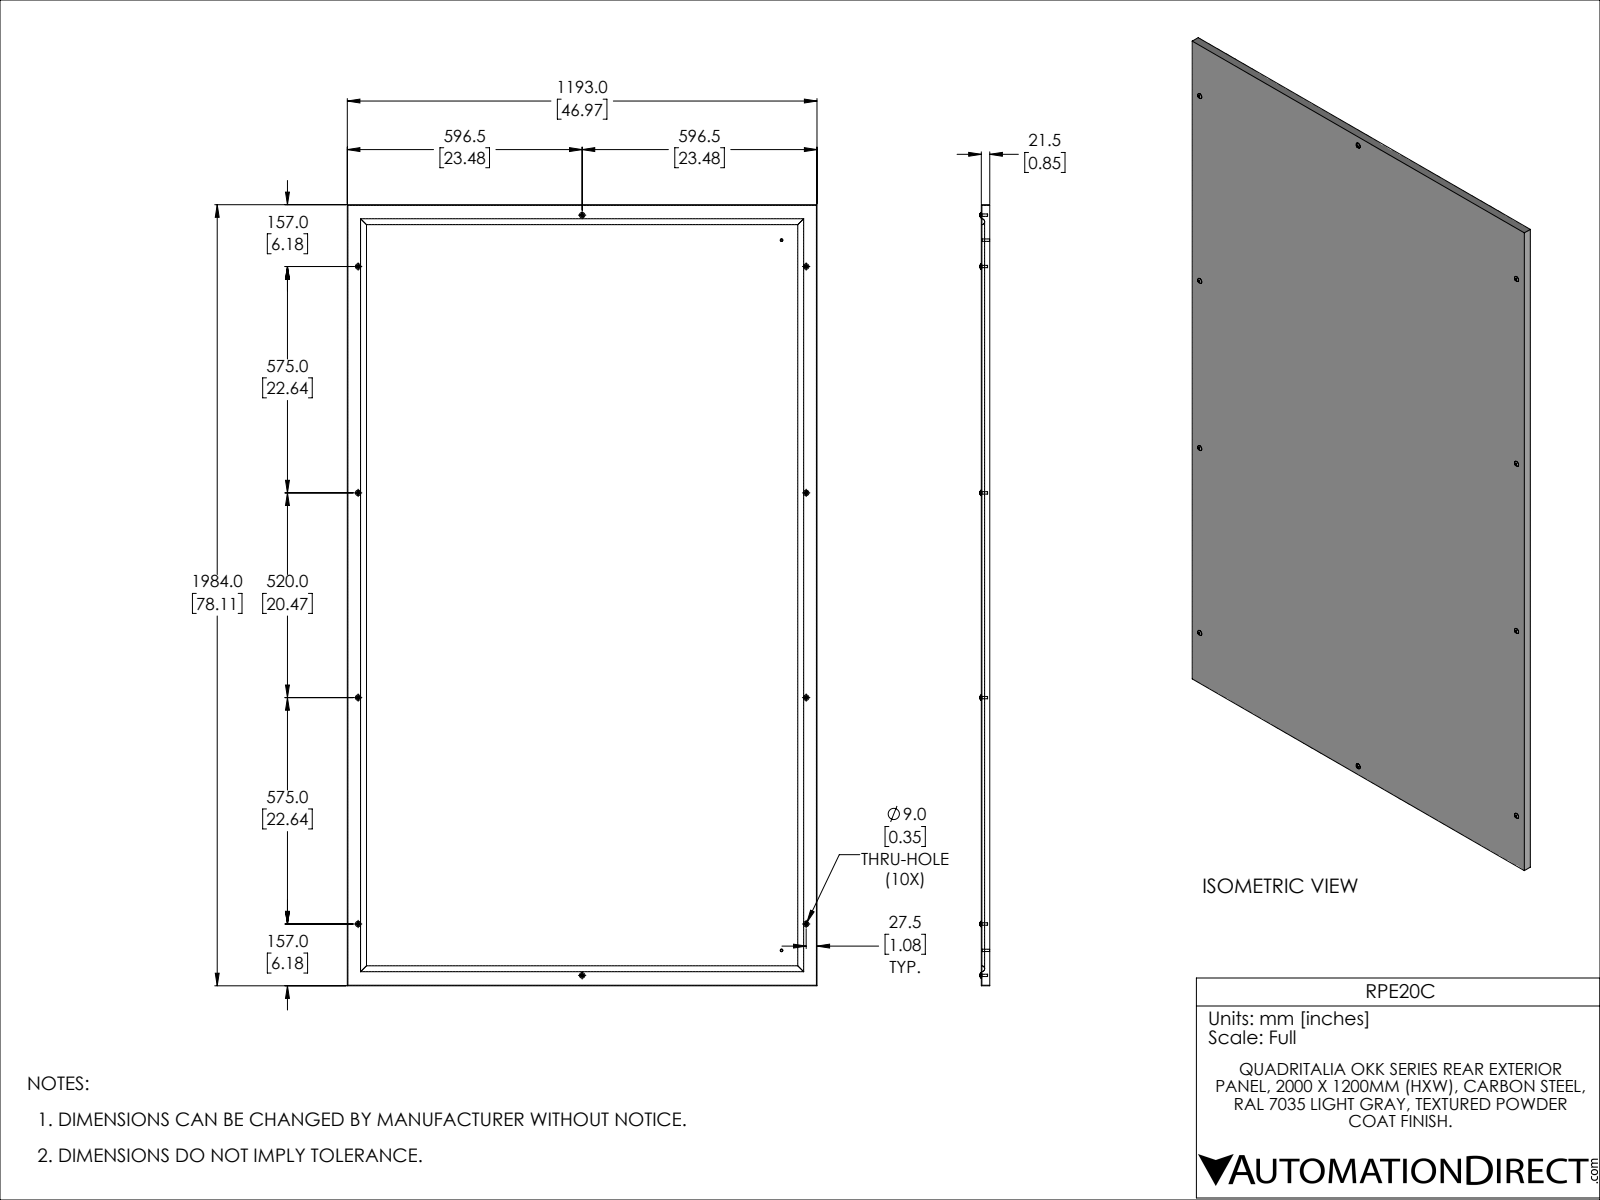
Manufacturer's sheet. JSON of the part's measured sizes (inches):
{"part_name": "RPE20C", "step_written_by": "SolidWorks 2021 (CONFIG_CONTROL_DESIGN)", "units": "inches", "bodies": {"solids": 17, "faces": 379, "planar": 189, "cylindrical": 158, "other": 32}, "overall_size": [78.11, 46.969, 0.992], "volume_in3": 258.5, "surface_area_in2": 8109, "round_holes": [[0.354, 10]], "round_bosses_or_shafts": [[0.236, 12], [0.551, 10], [0.276, 2]], "partial_cylinders_radius": [[0.02, 120], [0.296, 4]], "face_to_face_distances": [0.059, 46.909, 78.051, 46.969, 46.85, 78.11, 77.992, 0.846, 0.787, 21.906], "hole_center_spacings": [22.638, 22.983, 35.683, 43.11, 44.803, 50.198, 53.195, 62.176]}
